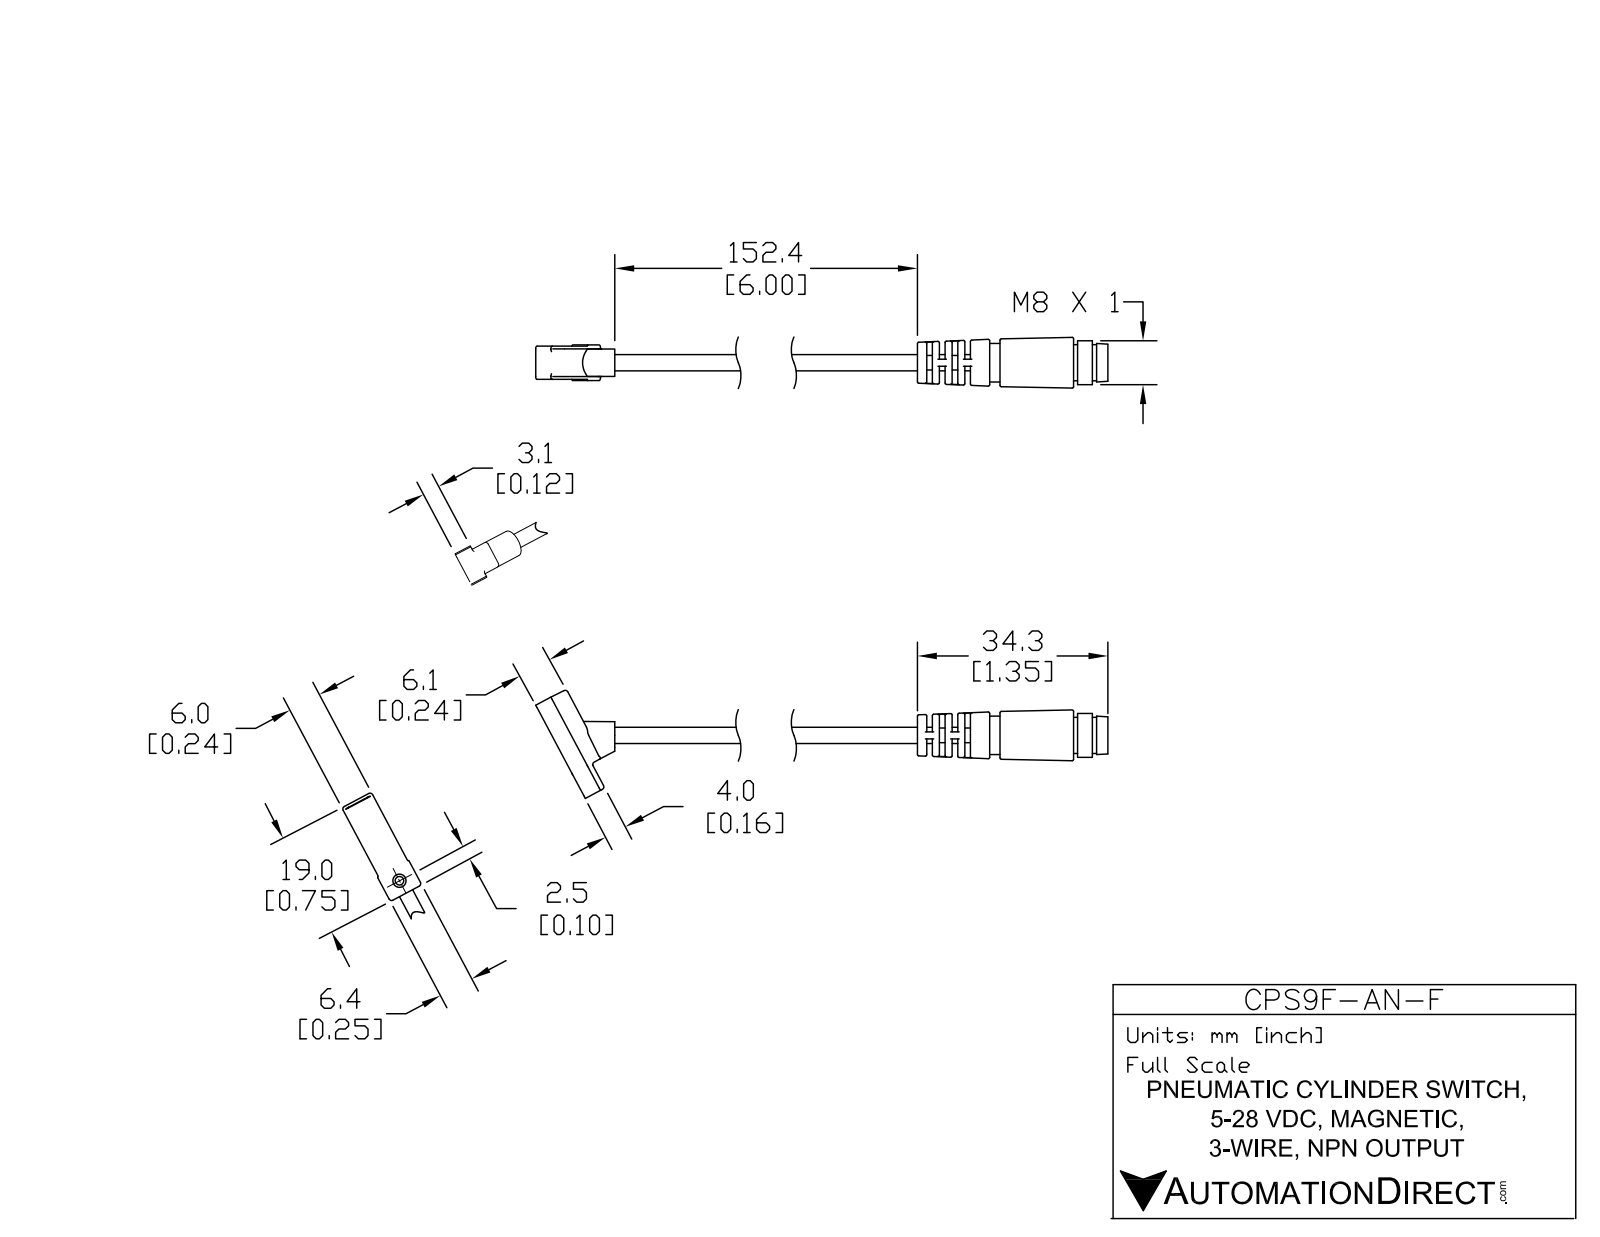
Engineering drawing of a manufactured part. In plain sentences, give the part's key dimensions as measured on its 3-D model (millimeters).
The part is named "CPS9F-AN-F". Its 3-D file was written by "SolidWorks 2014 (AUTOMOTIVE_DESIGN)". It is 5 solids with 257 faces: 85 planar, 96 cylindrical and 76 other. Overall it measures 143.4 by 84.5 by 9.1 millimeters. Its volume is 2 980 cubic millimeters and its surface area 3 091 square millimeters. Round holes: 1 of diameter 2.4, 1 of diameter 5.8. Round bosses or shafts: 3 of diameter 1, 1 of diameter 7.9, 1 of diameter 6.9, 1 of diameter 6.5, 1 of diameter 2.9, 1 of diameter 2.9. Partial cylindrical surfaces (rounded edges, fillets, slot ends): 23 of radius 0.1, 18 of radius 0.5, 2 of radius 0.2, 2 of radius 0.6, 1 of radius 2.5. The main face-to-face distances are 1.3, 2.3, 4.6, 0.5, 1, 2.3, 3.3, 5, 5.5, 1.
